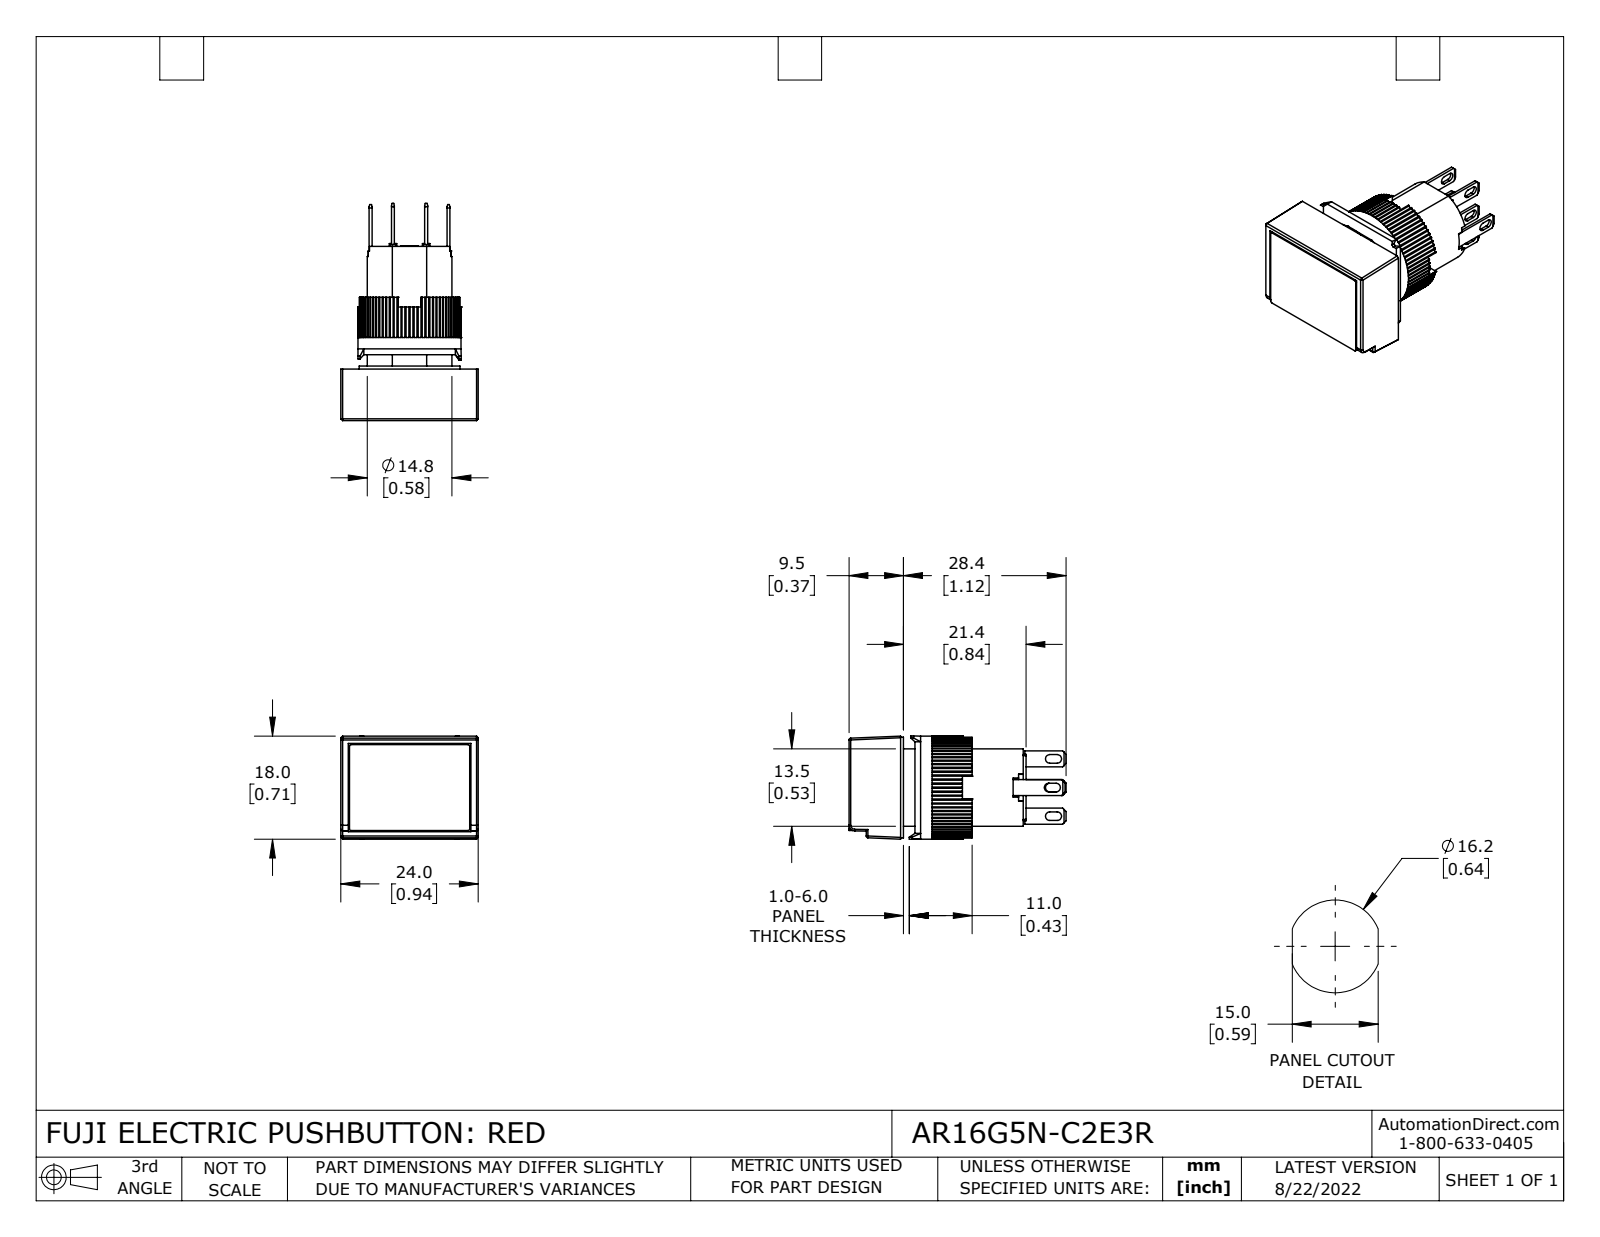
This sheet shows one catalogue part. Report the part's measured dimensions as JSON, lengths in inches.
{"part_name": "AR16G5N-C2E3R", "step_written_by": "SolidWorks 2021 (CONFIG_CONTROL_DESIGN)", "units": "inches", "bodies": {"solids": 14, "faces": 841, "planar": 654, "cylindrical": 181, "other": 6}, "overall_size": [1.492, 0.945, 0.709], "volume_in3": 0.448, "surface_area_in2": 9.503, "round_holes": [[0.543, 1], [0.583, 1]], "round_bosses_or_shafts": [[0.709, 1], [0.693, 1]], "partial_cylinders_radius": [[0.01, 80], [0.008, 12], [0.03, 8], [0.012, 6], [0.039, 1]], "face_to_face_distances": [0.213, 0.354, 0.142, 0.35, 0.492, 0.138, 0.02, 0.843, 0.059, 0.453]}
